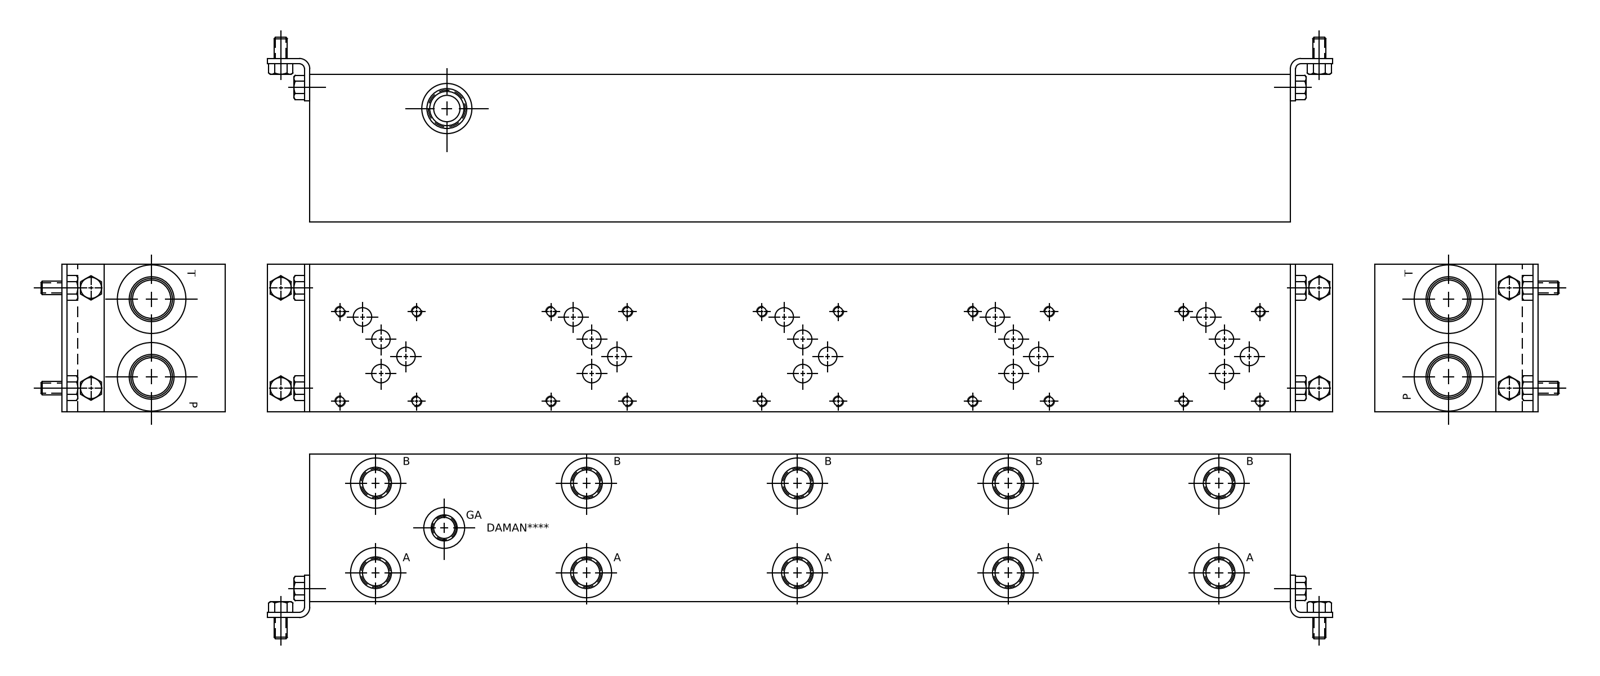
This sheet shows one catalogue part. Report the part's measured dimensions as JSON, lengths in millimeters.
{"part_name": "Part_AD05P055S~C_3D", "step_written_by": "Autodesk Inventor 2019 (AUTOMOTIVE_DESIGN)", "units": "millimeters", "bodies": {"solids": 1, "faces": 943, "planar": 466, "cylindrical": 149, "other": 328}, "overall_size": [590.55, 88.9, 88.9], "volume_mm3": 4486000, "surface_area_mm2": 266505, "round_holes": [[5.11, 20], [6.35, 20], [11.13, 20], [15.88, 10], [17.5, 10], [19.05, 10], [19.25, 10], [30.63, 10], [6.53, 2], [7.92, 2], [23.01, 2], [24.92, 2]], "face_to_face_distances": [88.9, 0.79, 590.55, 88.11, 589.76, 588.97, 19.05, 15.06, 14.27, 73.84], "hole_center_spacings": [127, 254, 138, 381, 46.05, 53.98, 70.95, 137.98]}
